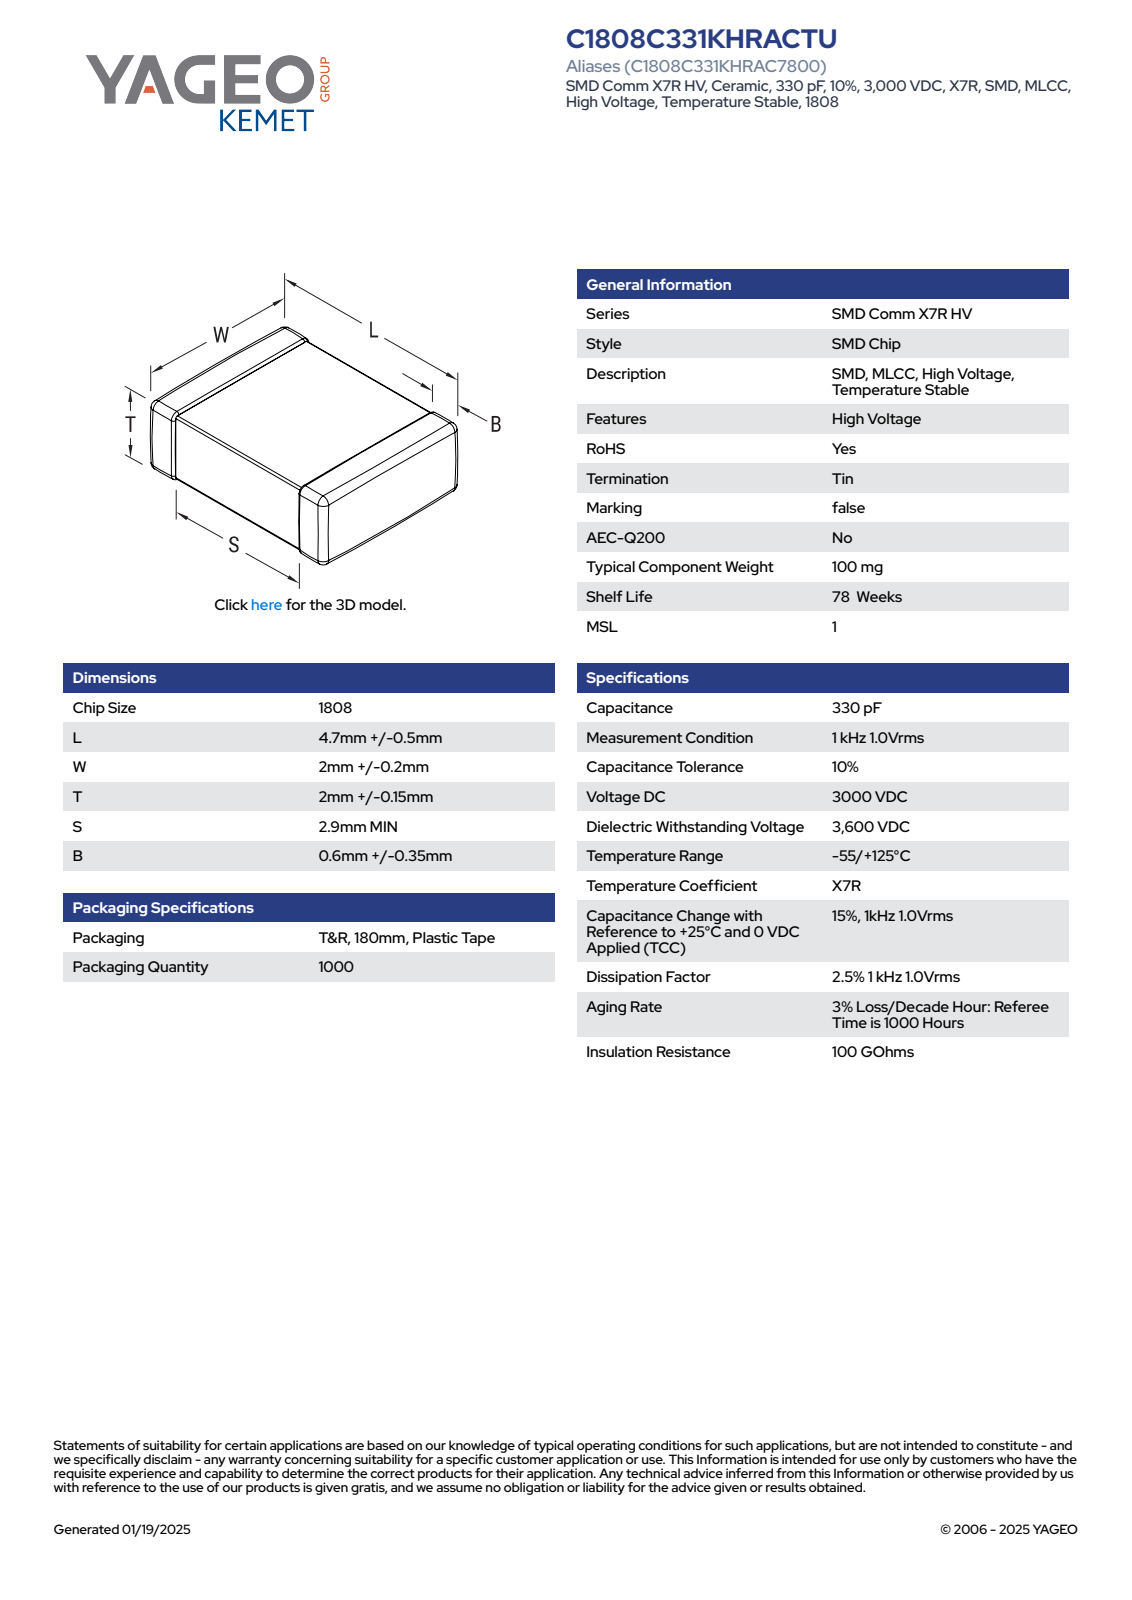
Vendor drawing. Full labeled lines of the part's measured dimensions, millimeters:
Part name (STEP PRODUCT): CCS_CCSTD_1808_L5.2W2.2T2.15B0.6
STEP written by: SolidWorks 2021 (AUTOMOTIVE_DESIGN)
Units: millimetres
Bodies: 4 solids, 125 faces (71 planar, 38 cylindrical, 16 other)
Overall size (bounding box): 5.2 × 2.2 × 2.15
Volume: 23 mm³ · Surface area: 54 mm²
Main face-to-face distances: 2.1, 2.15, 2.05, 5.2, 2.2, 2.11, 2.06, 0.33, 2.48, 2.72
